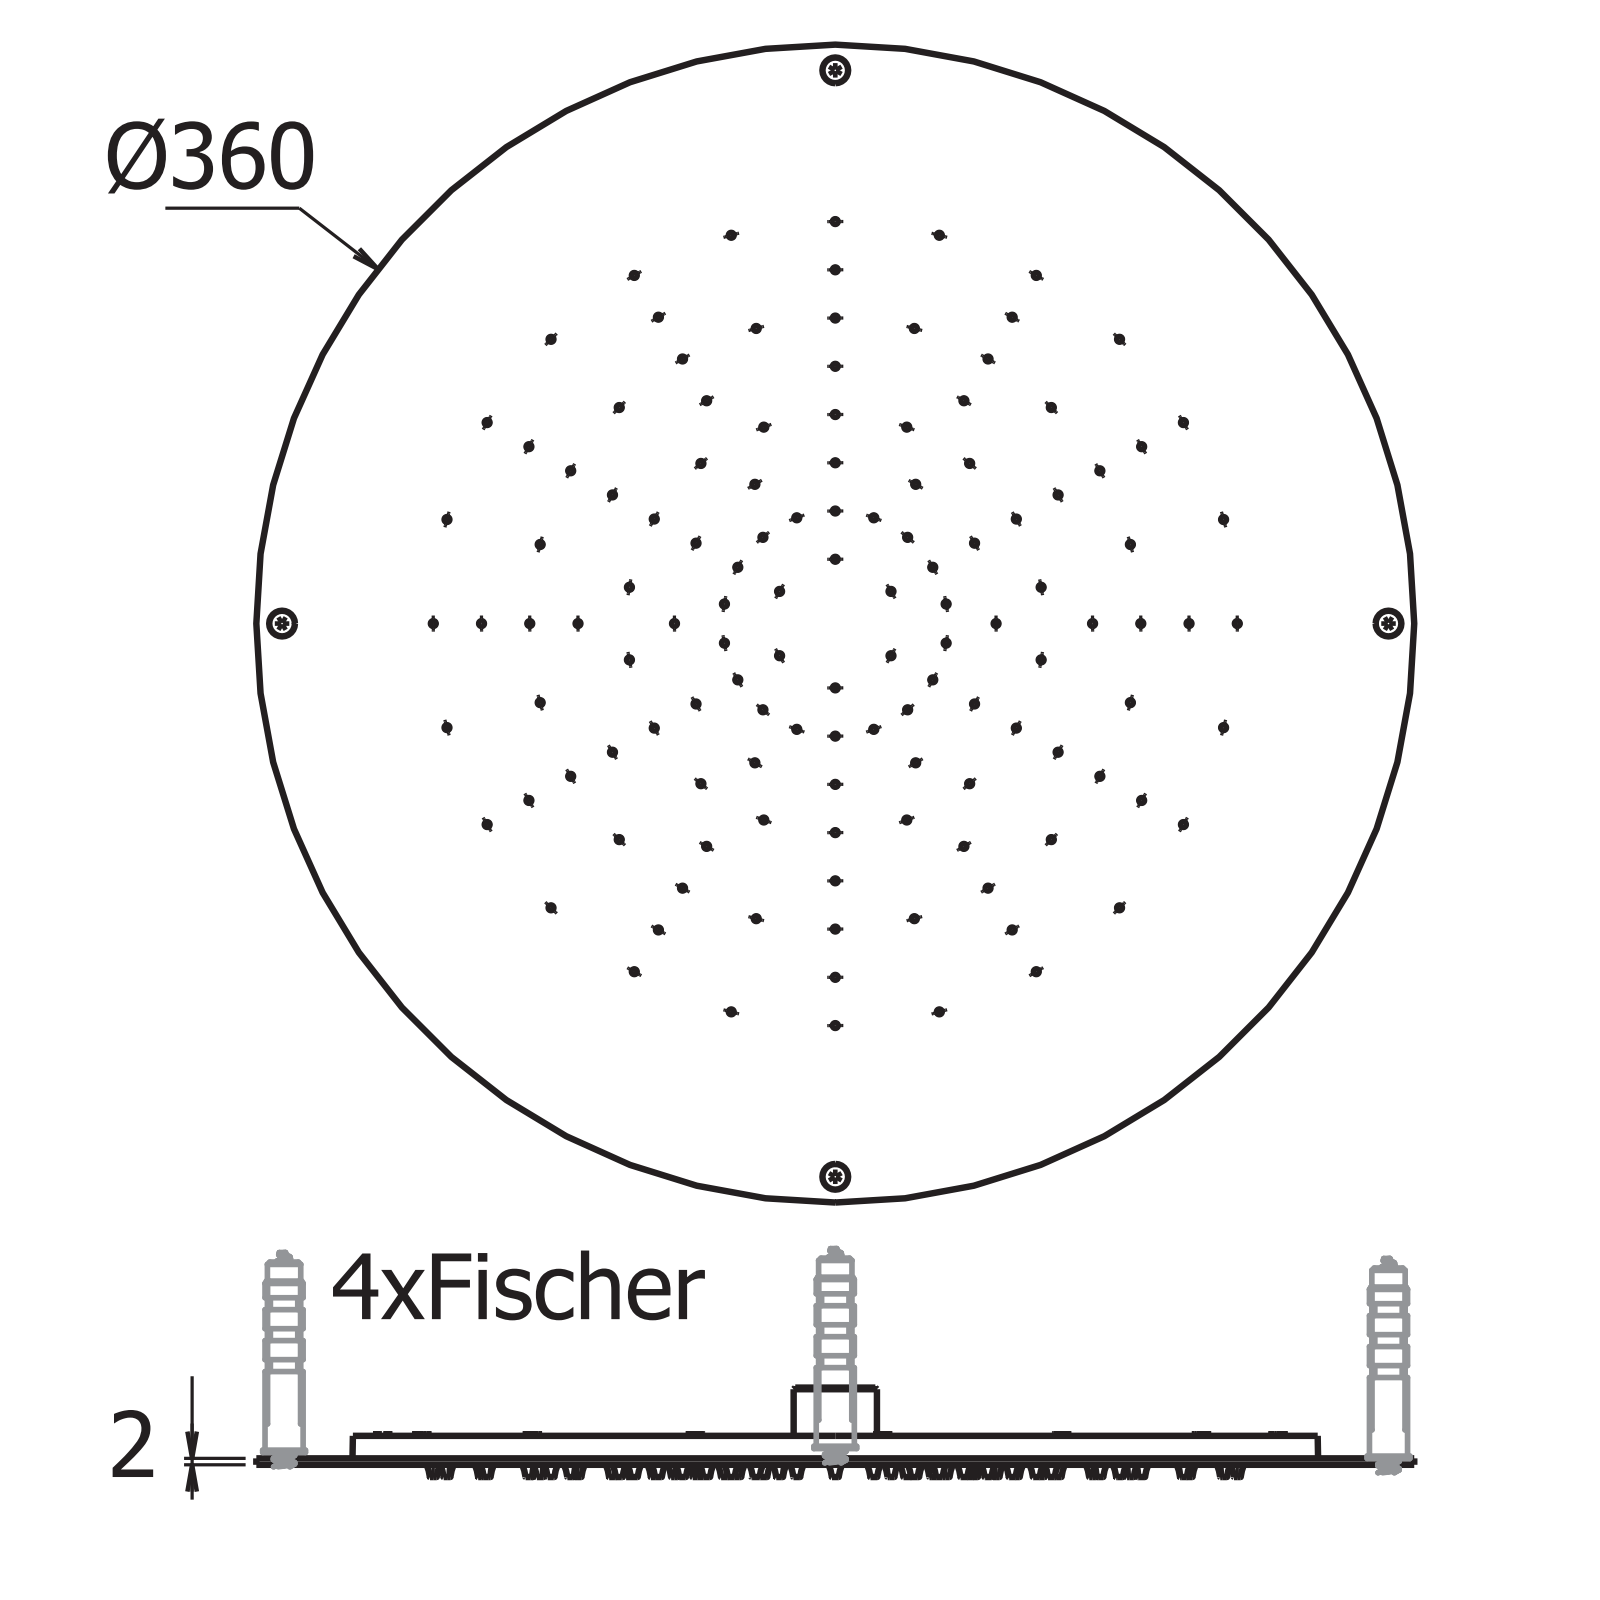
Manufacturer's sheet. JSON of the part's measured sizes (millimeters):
{"part_name": "A.R._24532/20220905", "step_written_by": "Spatial InterOp 3D (AUTOMOTIVE_DESIGN)", "units": "millimeters", "bodies": {"solids": 1, "faces": 2933, "planar": 773, "cylindrical": 696, "other": 1464}, "overall_size": [360.04, 360.04, 27.8], "volume_mm3": 352324, "surface_area_mm2": 390455, "round_holes": [[1.5, 126], [1.7, 126], [7, 19], [2.5, 15], [3.2, 15], [5.1, 15], [14, 1], [16.4, 1], [18.63, 1], [28.2, 1], [271, 1], [283.4, 1]], "round_bosses_or_shafts": [[10, 126], [6, 15], [5, 15], [4.3, 15], [3, 15], [360.04, 1], [295.6, 1], [285.4, 1]], "partial_cylinders_radius": [[0.3, 32], [20, 15]], "face_to_face_distances": [2, 7, 9, 1, 6, 8, 3, 1.4, 3.4, 4.6], "hole_center_spacings": [267.72, 58.53, 165.46, 279.95, 15, 114.5, 209.19, 243.78]}
